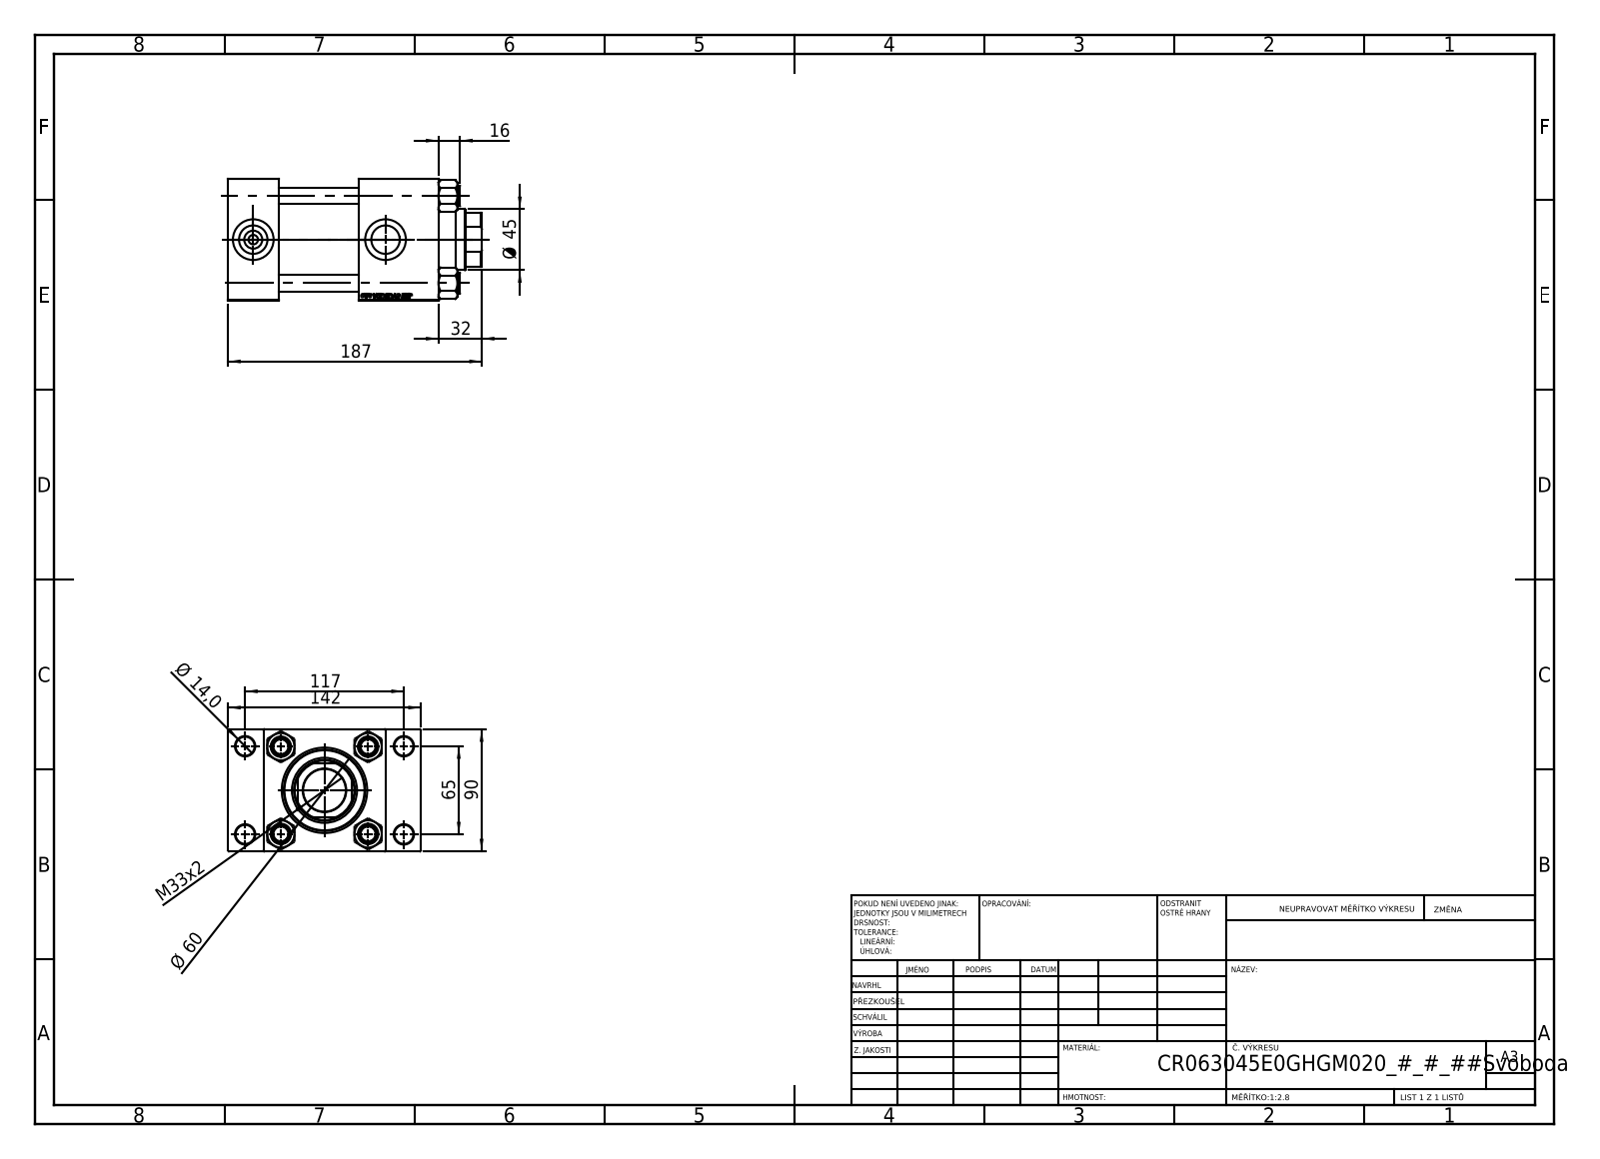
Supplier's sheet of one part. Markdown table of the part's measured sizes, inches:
| quantity | value |
| --- | --- |
| part name | V215CR_TYCINKA_E; V215CR_E_Body; V215_VC_A; NUT_M5_E (+1 more) |
| STEP written by | SolidWorks 2019 (CONFIG_CONTROL_DESIGN) |
| units | inches |
| bodies | 11 solids, 1133 faces (497 planar, 84 cylindrical, 552 other) |
| overall size | 7.362 × 5.591 × 3.543 |
| volume | 70.6 in³ |
| surface area | 337.3 in² |
| round holes (diameter × count) | 0.472 × 4, 0.551 × 4, 0.276 × 2, 0.825 × 2, 1.181 × 2, 1.24 × 1, 1.772 × 1, 1.89 × 1, 1.969 × 1, 2.362 × 1, 2.48 × 1 |
| round bosses / shafts (diameter × count) | 0.591 × 4, 2.717 × 1 |
| partial cylindrical surfaces (radius × count) | 0.866 × 1 |
| main face-to-face distances | 3.543, 1.457, 2.323, 1.024, 4.567, 6.102, 4.646, 3.78, 5.591, 4.972 |
| hole center spacings | 1.037, 1.79, 2.531, 2.635, 2.748, 3.569, 4.383, 2.559 |
